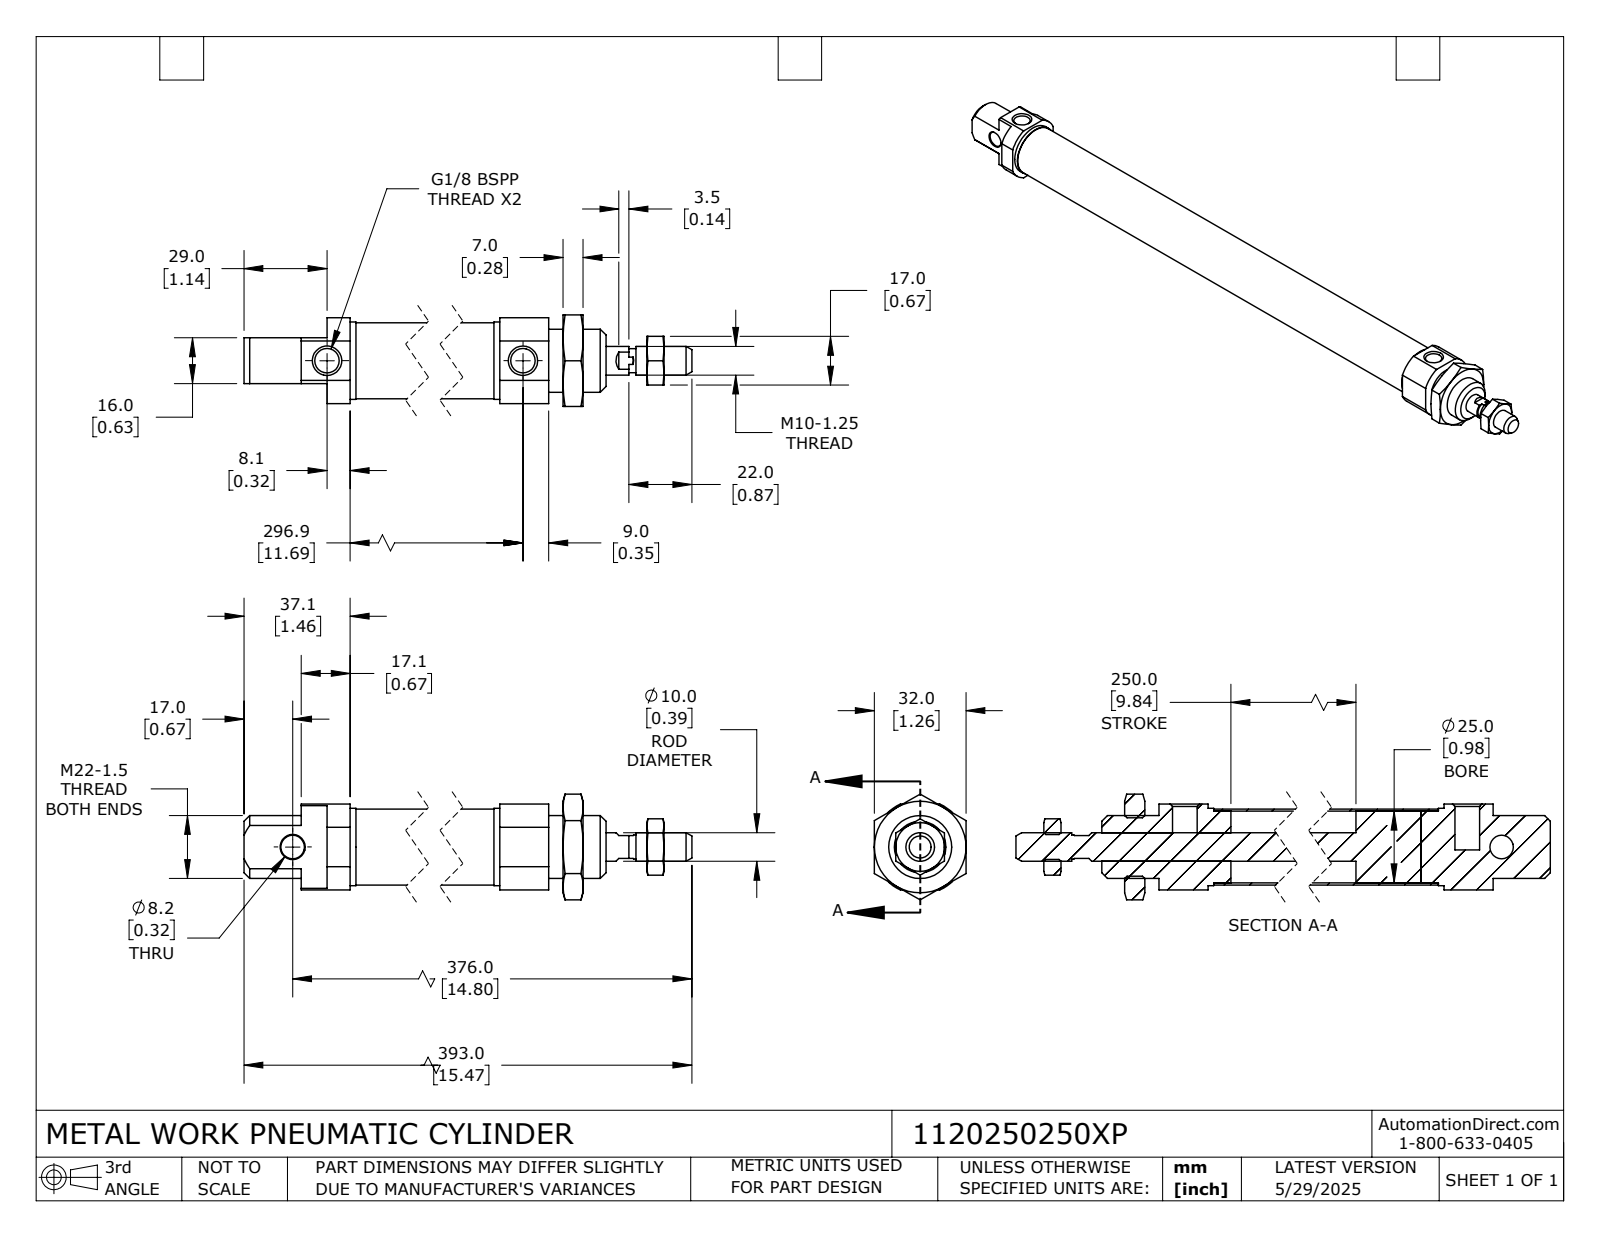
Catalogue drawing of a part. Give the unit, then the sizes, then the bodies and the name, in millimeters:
Units: millimetres
Overall size (bounding box): 393 × 36.95 × 32
Round holes (diameter × count): ⌀8.57 ×2, ⌀8.2 ×1, ⌀8.65 ×1, ⌀20.38 ×1, ⌀25 ×1
Round bosses / shafts (diameter × count): ⌀27 ×1, ⌀26.52 ×1, ⌀25.15 ×1, ⌀22 ×1, ⌀10 ×1, ⌀8.4 ×1
Partial cylindrical surfaces — rounded edges, fillets, slot ends (radius × count): R16.5 ×1
Main face-to-face distances: 7, 8, 37.1, 23, 30, 317.9, 297.9, 25.1, 16, 280.8
Hole centre spacings: 305
Volume: 99 627 mm³ · Surface area: 74 875 mm²
Bodies: 6 solids, 144 faces (54 planar, 44 cylindrical, 46 other)
Part name (STEP PRODUCT): 1120250250XP_ROD; 1120250250XP; 1120250250XP_BODY
STEP written by: SolidWorks 2024 (CONFIG_CONTROL_DESIGN)
